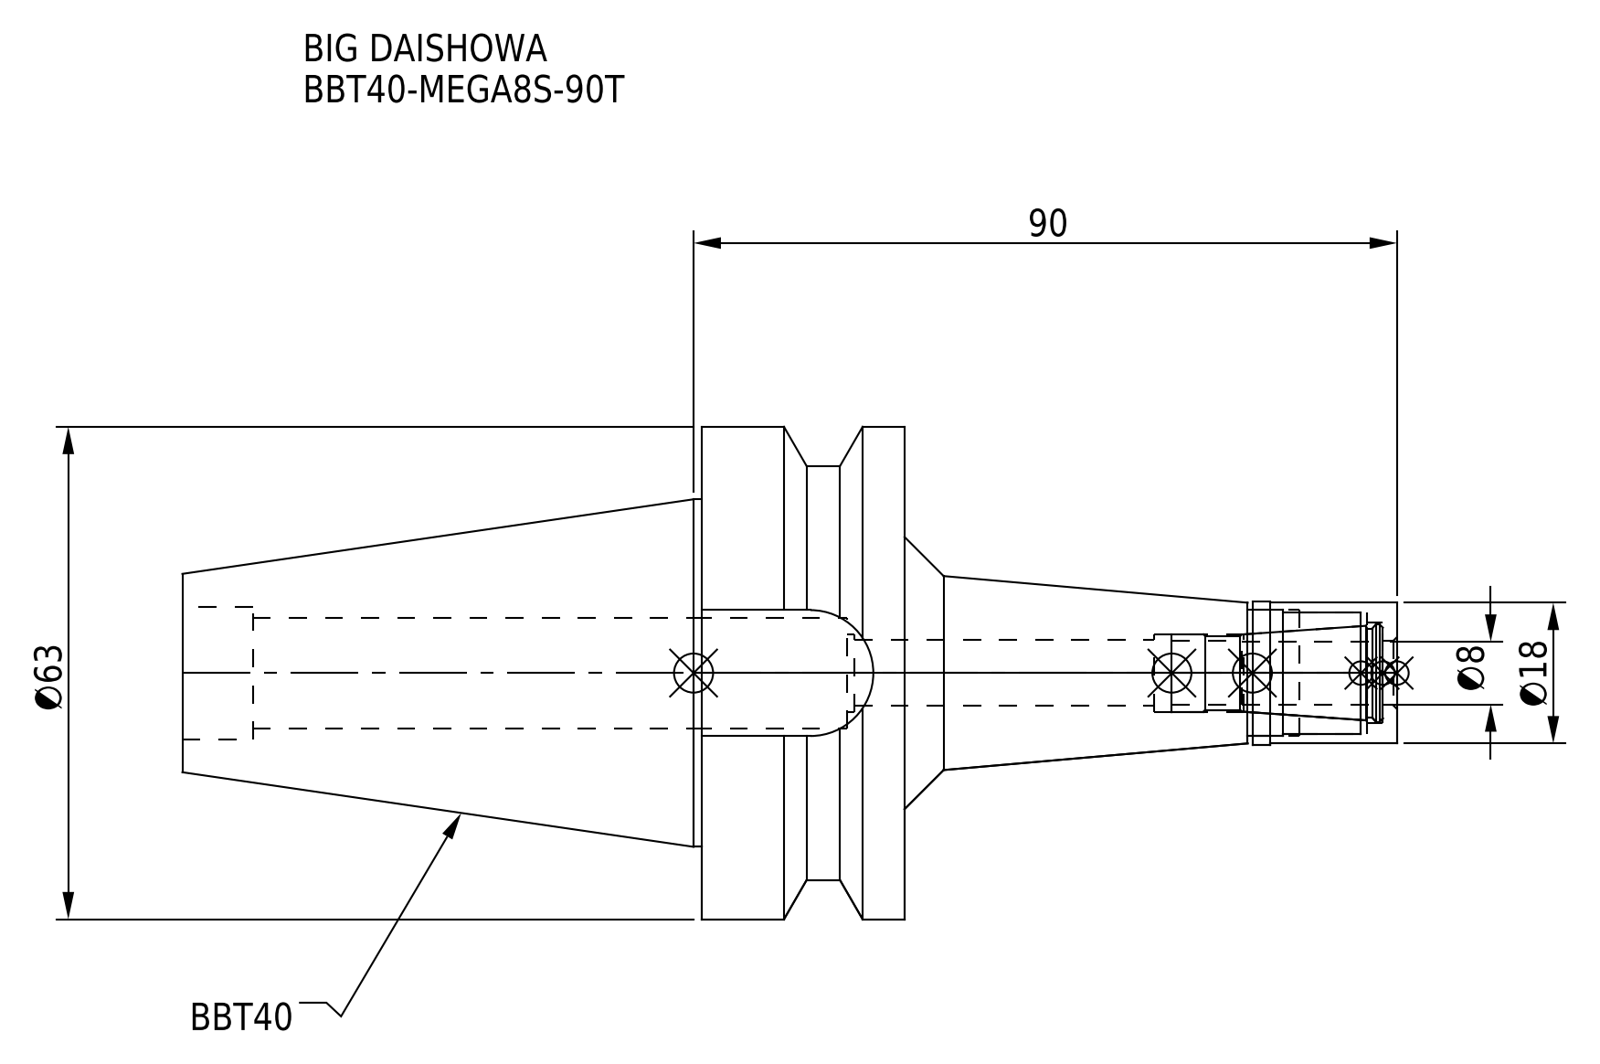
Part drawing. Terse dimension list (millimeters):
name: BBT40-MEGA8S-90T_1.stp; DXF_TEMP_ASSY_ASM_4_ASM.stp; BBT40MS08090T-080_ASM.stp; BBT40-MEGA8S-90T (+3 more)
written by: SolidWorks 2019 (CONFIG_CONTROL_DESIGN)
unit: mm
bodies: 2 solids, 74 faces (22 planar, 38 cylindrical, 14 other)
size: 155.4 × 63 × 63
volume: 138 943 mm³; area: 30 080 mm²
holes: 1× ⌀8.2, 1× ⌀8.4, 1× ⌀9.9, 1× ⌀10, 1× ⌀12.9, 1× ⌀14.2, 1× ⌀15.6, 1× ⌀16.1, 1× ⌀17
bosses: 1× ⌀63, 1× ⌀53, 1× ⌀44.45, 1× ⌀18.3, 1× ⌀18
rounds: 1× R8.05
face distances: 26, 45, 92.4, 66.4, 16.1, 63, 89, 155.4, 18.6, 70.4
